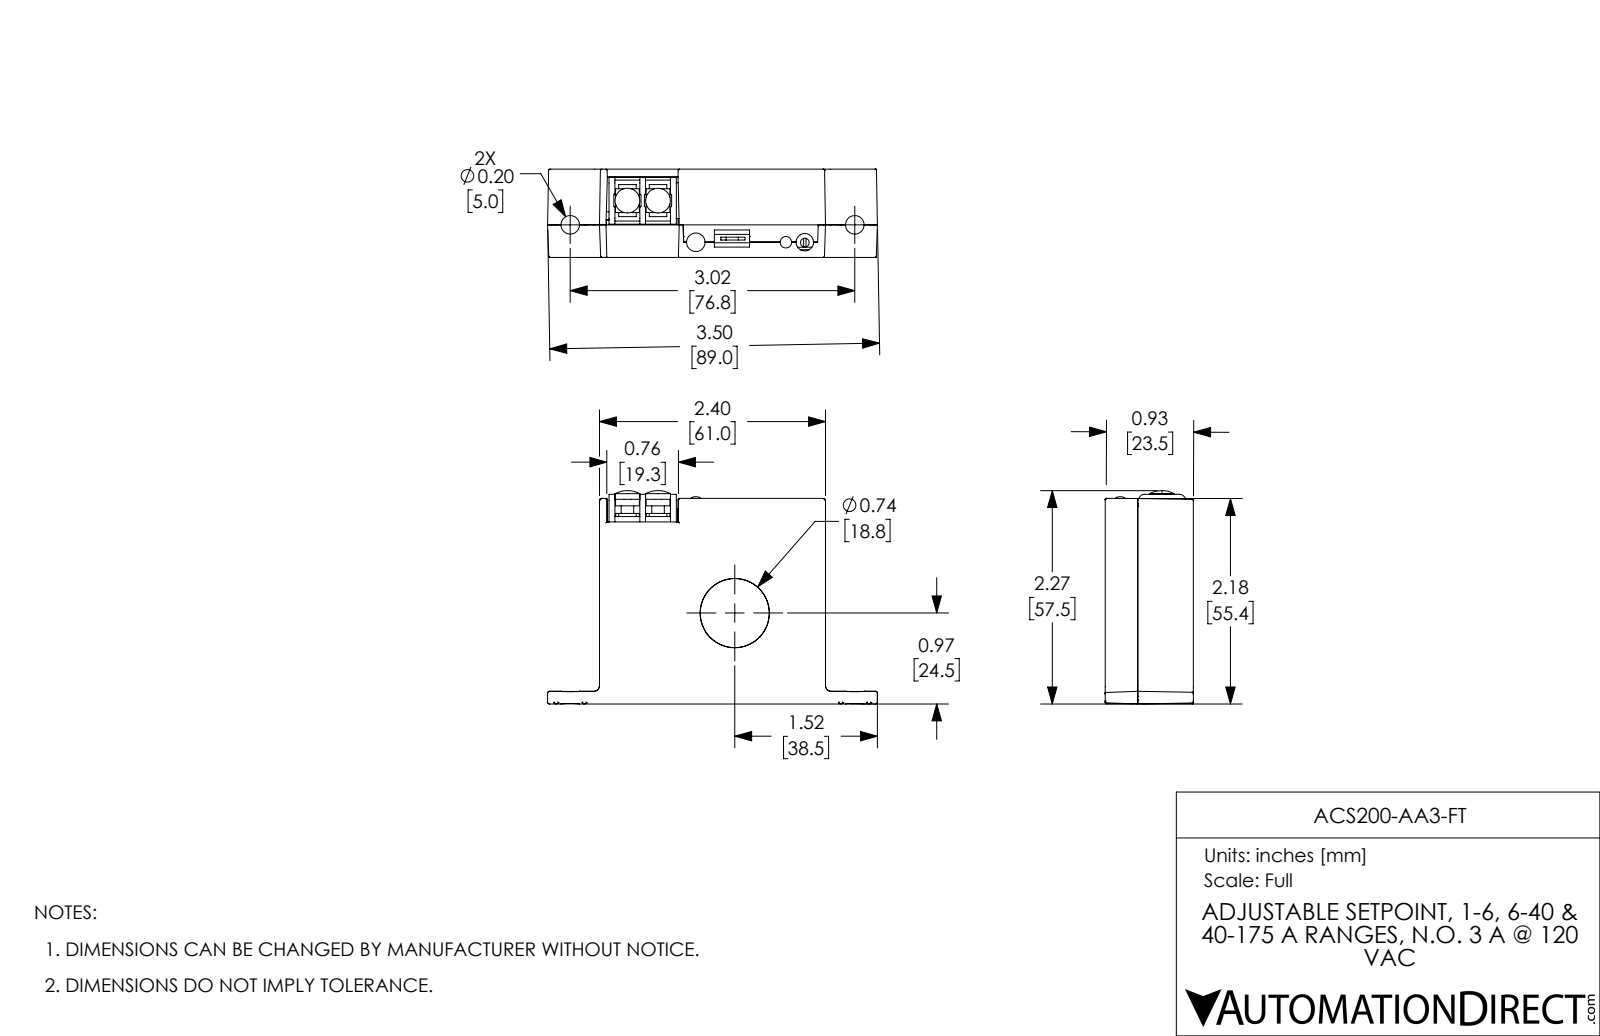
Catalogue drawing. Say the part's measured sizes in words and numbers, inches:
The part is named "ACS200-AA3-FT". Its 3-D file was written by "SolidWorks 2017 (AUTOMOTIVE_DESIGN)". It is 8 solids with 550 faces: 360 planar, 126 cylindrical and 64 other. Overall it measures 3.504 by 2.265 by 0.937 inches. Its volume is 1.893 cubic inches and its surface area 53.16 square inches. Round holes: 4 of diameter 0.045, 3 of diameter 0.197, 2 of diameter 0.147, 1 of diameter 0.122, 1 of diameter 0.185, 1 of diameter 0.82. Round bosses or shafts: 4 of diameter 0.043, 2 of diameter 0.263, 2 of diameter 0.134, 1 of diameter 0.807, 1 of diameter 0.234, 1 of diameter 0.194, 1 of diameter 0.093. Partial cylindrical surfaces (rounded edges, fillets, slot ends): 20 of radius 0.012, 12 of radius 0.02, 8 of radius 0.03, 4 of radius 0.059, 2 of radius 0.008, 2 of radius 0.063. The main face-to-face distances are 0.083, 0.854, 0.937, 0.772, 0.442, 0.349, 0.413, 0.266, 0.33, 0.064. The hole center spacings are 2.151, 3.535, 0.201, 0.325, 0.563, 0.598, 0.66, 0.755.
